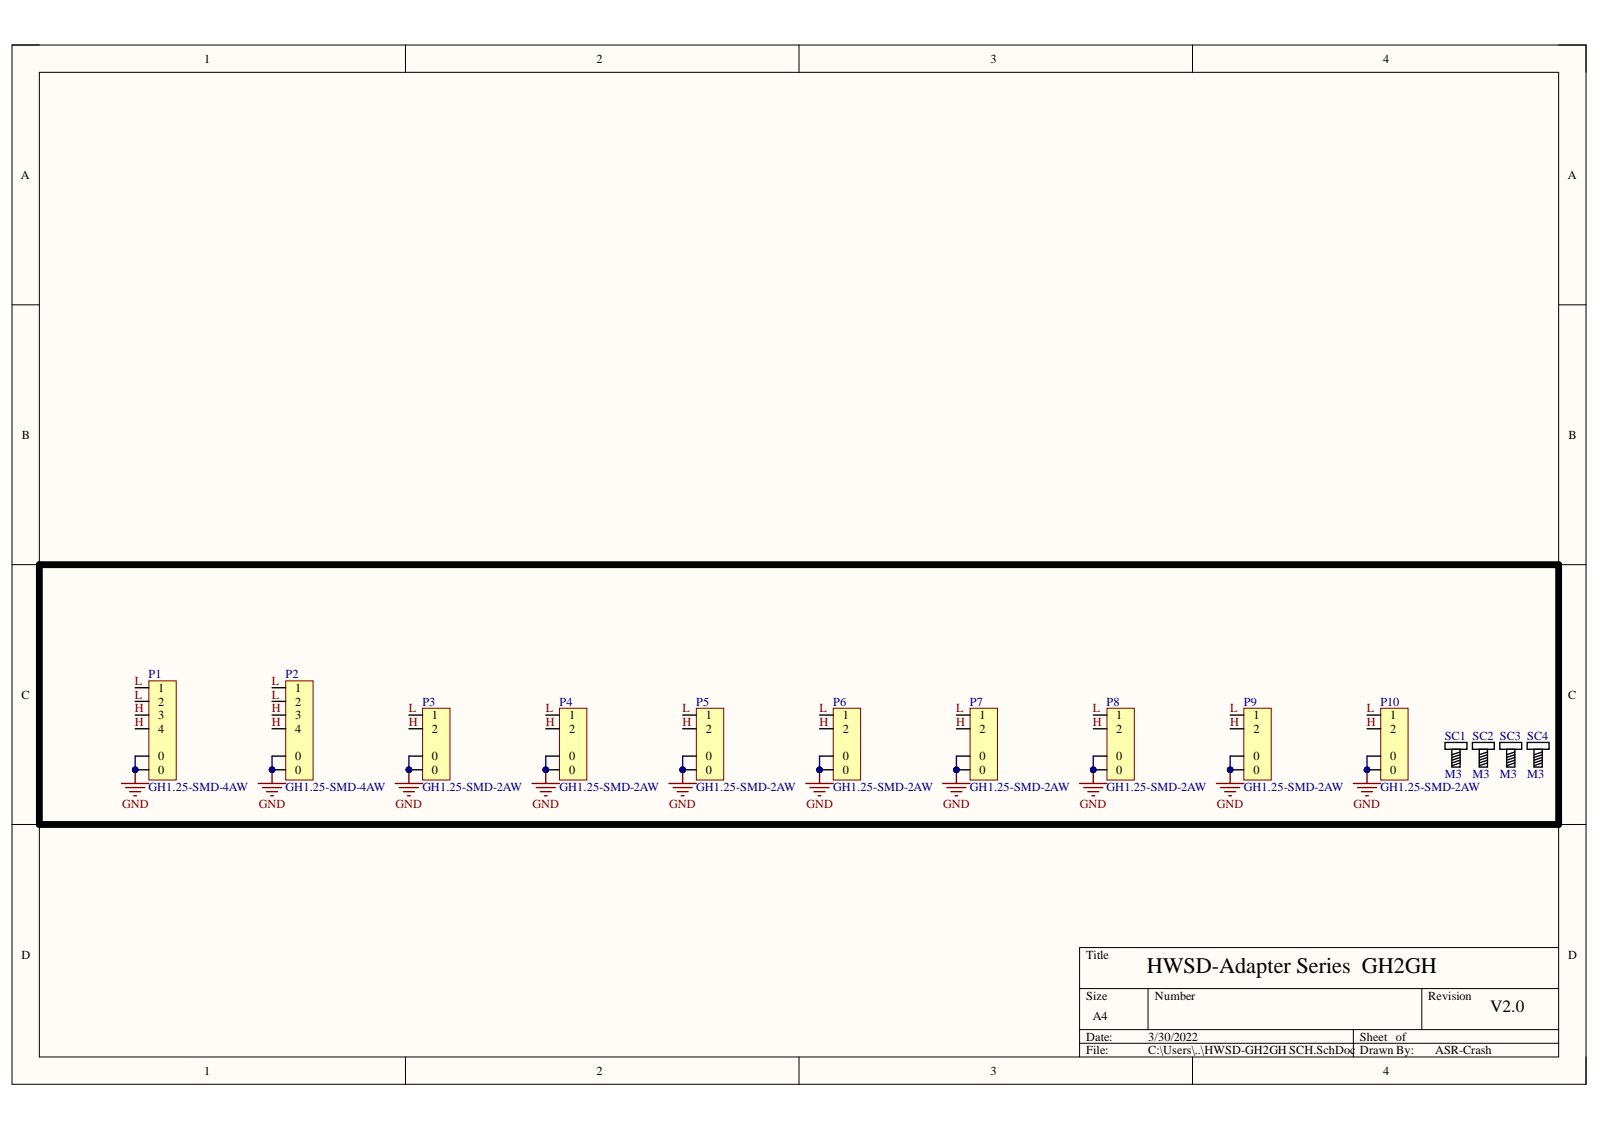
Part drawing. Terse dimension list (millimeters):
name: PCB; Board; P10; JST_GH_SM02B-GHS-TB_1x02-1MP_P1.25mm_Horizontal (+7 more)
written by: Open CASCADE 6.8 (AUTOMOTIVE_DESIGN)
unit: mm
bodies: 11 solids, 1548 faces (1540 planar, 8 cylindrical, 0 other)
size: 40 × 20 × 5.94
volume: 1 980 mm³; area: 4 032 mm²
holes: 4× ⌀3
rounds: 4× R2.54
face distances: 1.69, 5.94, 4.25, 1.85, 1.68, 4.26, 3.84, 5.75, 7.6, 4.05
hole spacings: 14.92, 34.92, 37.97
